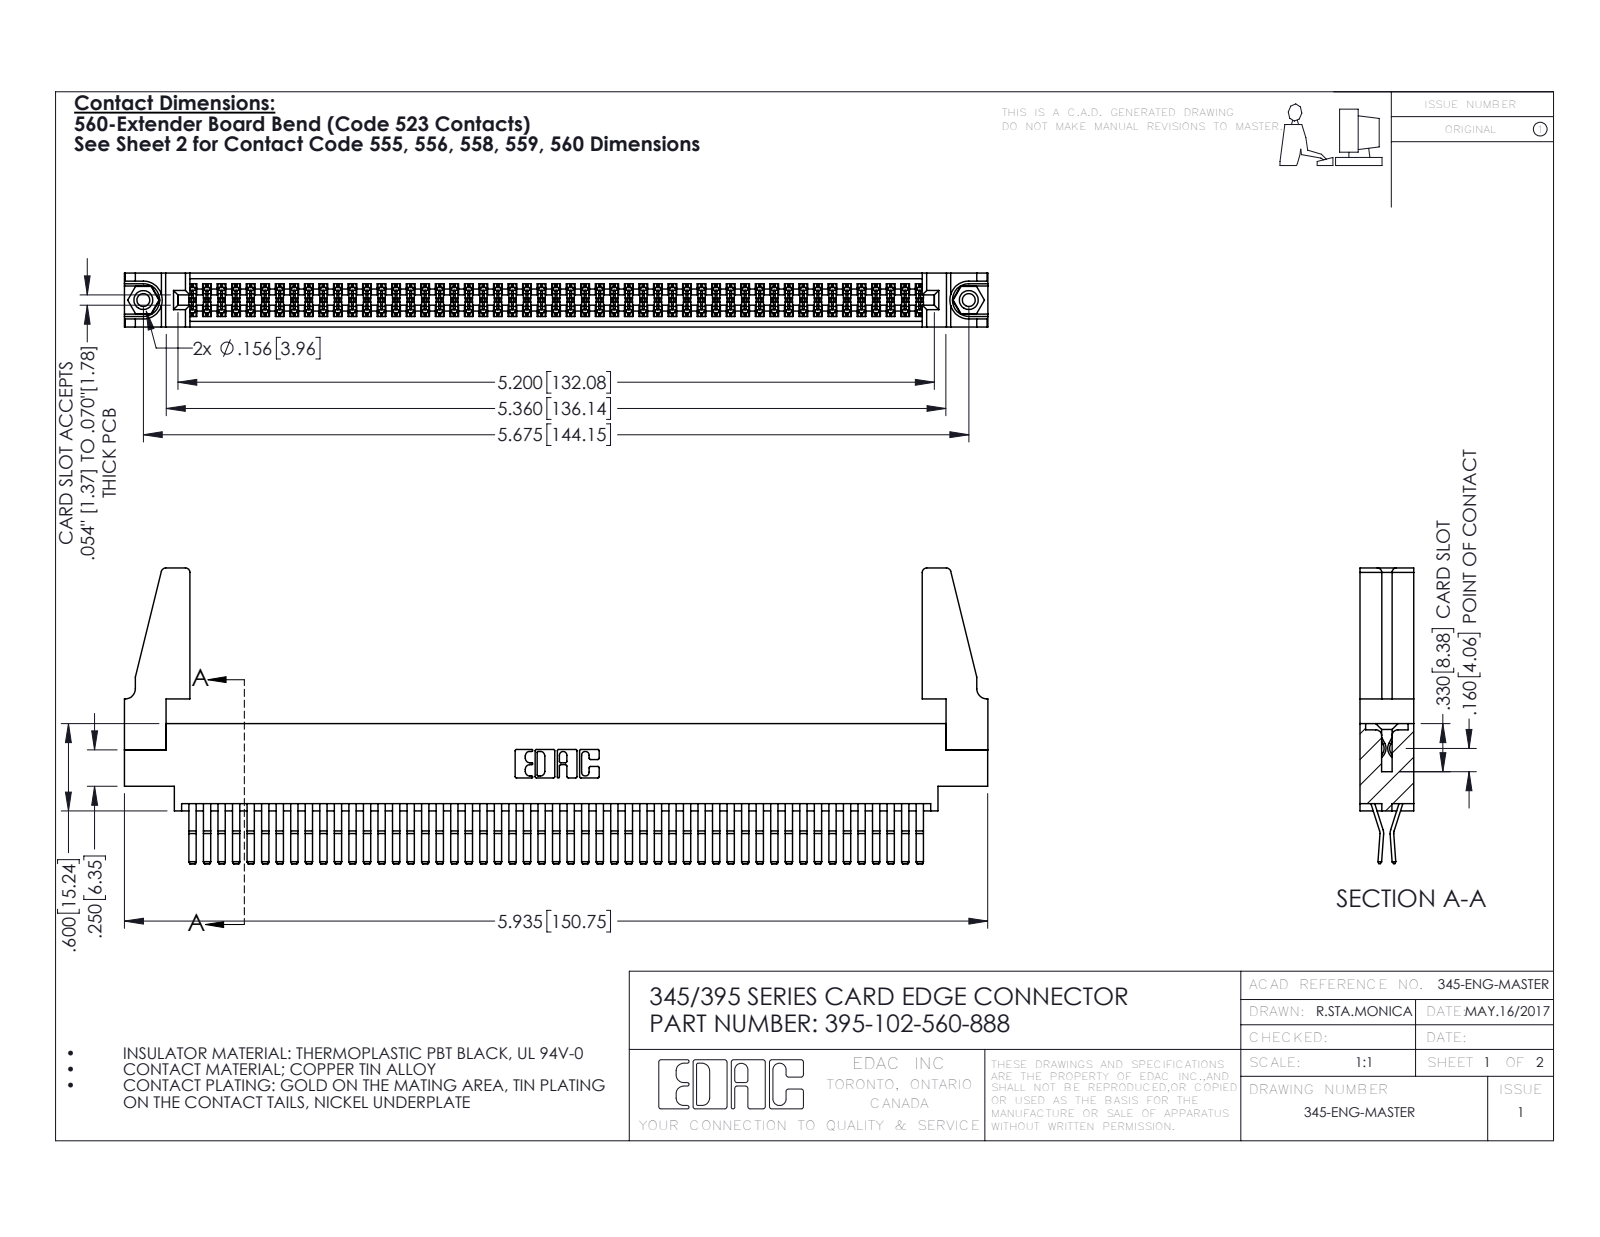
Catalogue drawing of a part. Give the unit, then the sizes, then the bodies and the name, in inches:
Units: inches
Overall size (bounding box): 5.936 × 2.032 × 0.37
Round holes (diameter × count): ⌀0.089 ×2, ⌀0.125 ×2, ⌀0.156 ×2, ⌀0.064 ×1
Round bosses / shafts (diameter × count): ⌀0.155 ×2
Partial cylindrical surfaces — rounded edges, fillets, slot ends (radius × count): R0.006 ×154, R0.01 ×22, R0.03 ×8, R0.007 ×6, R0.031 ×6, R0.026 ×3, R0.01 ×2, R0.014 ×2
Main face-to-face distances: 0.072, 0.298, 0.025, 0.37, 0.2, 0.098, 0.272, 0.225, 0.175, 0.149
Hole centre spacings: 0.27, 5.439, 5.675
Volume: 1.131 in³ · Surface area: 43.02 in²
Bodies: 107 solids, 5558 faces (3522 planar, 2020 cylindrical, 16 other)
Part name (STEP PRODUCT): 395-102-560-888; 345 Part_0.170 Offset - 0.156 Dia-TH; 345-250-001_345-250-001-102; 345-292-001_560 Tail (+1 more)
STEP written by: SolidWorks 2016 (CONFIG_CONTROL_DESIGN)
